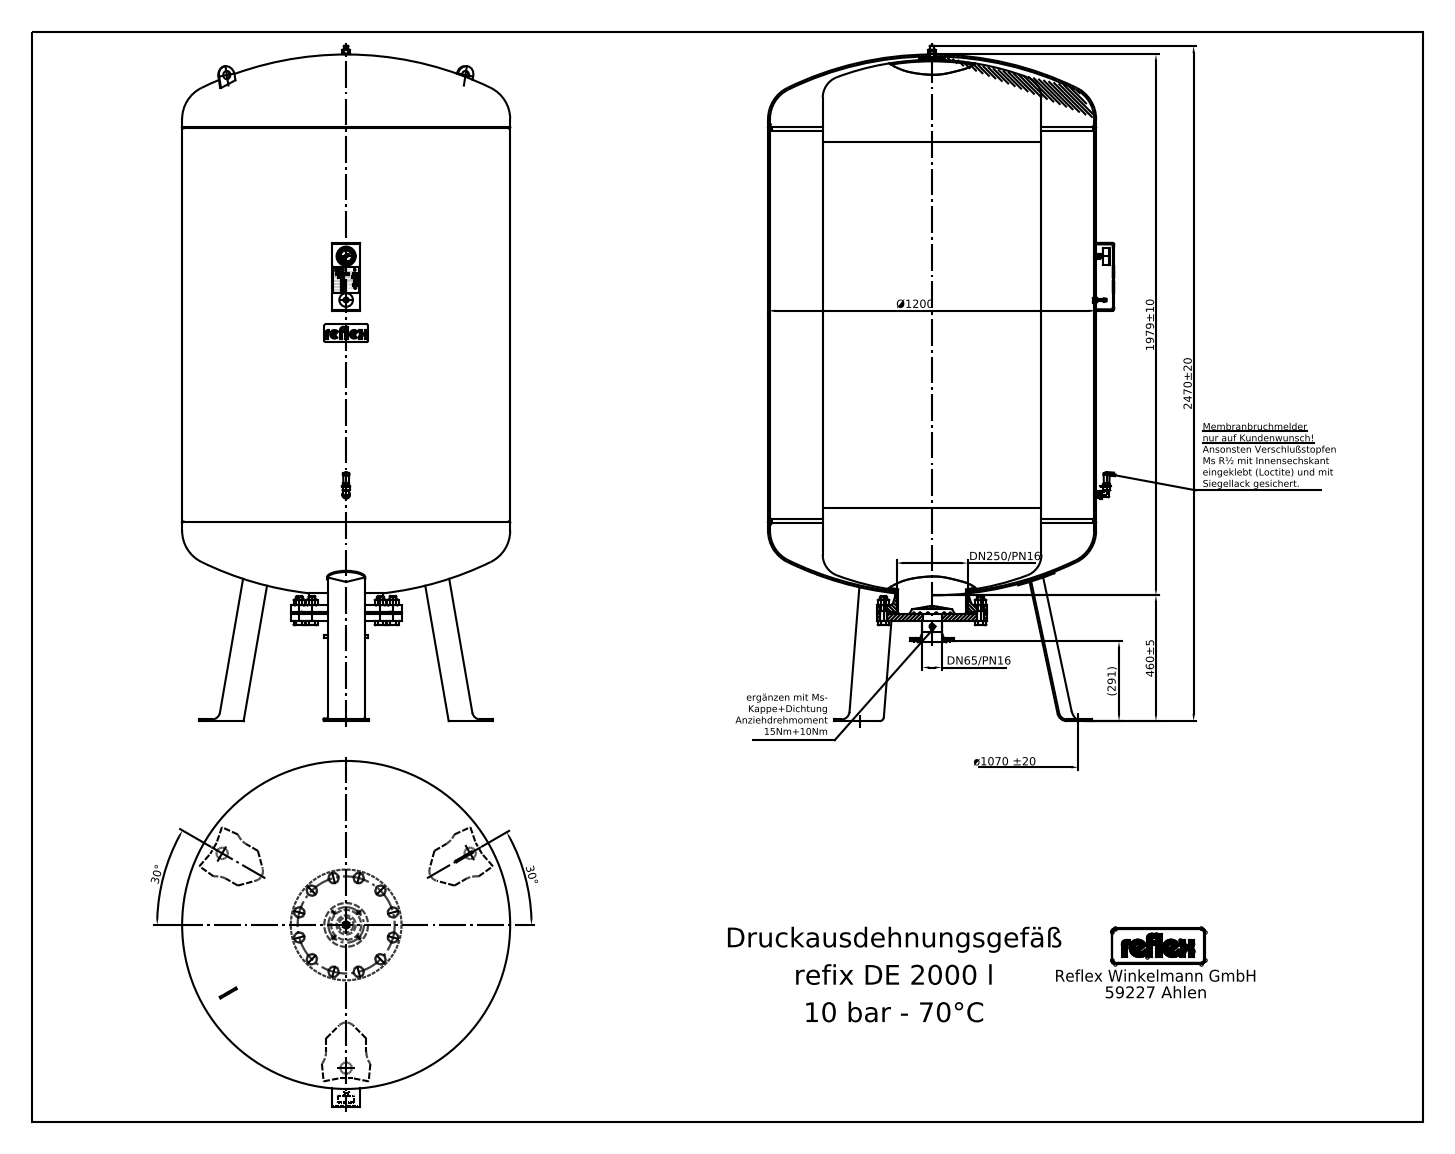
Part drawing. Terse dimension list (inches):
written by: Mechanical Desktop 2008 (CONFIG_CONTROL_DESIGN)
unit: in
bodies: 23 solids, 612 faces (340 planar, 155 cylindrical, 117 other)
size: 97.244 × 49.843 × 47.244
volume: 126 000 in³; area: 22 920 in²
holes: 1× ⌀0.394, 1× ⌀1.181, 1× ⌀1.969, 1× ⌀2.717, 1× ⌀10.252
bosses: 13× ⌀0.63, 2× ⌀1.102, 2× ⌀1.024, 2× ⌀0.787, 1× ⌀47.244, 1× ⌀15.945, 1× ⌀10.748, 1× ⌀2.996
rounds: 18× R0.984, 4× R0.221, 3× R0.089, 3× R0.354, 2× R0.039, 2× R0.151, 2× R0.197, 2× R0.266
face distances: 57.874, 1.024, 12.283, 70.157, 13.307, 71.181, 1.22, 0.235, 0.232, 2.244
hole spacings: 3.241, 24.232, 28.746, 31.187
